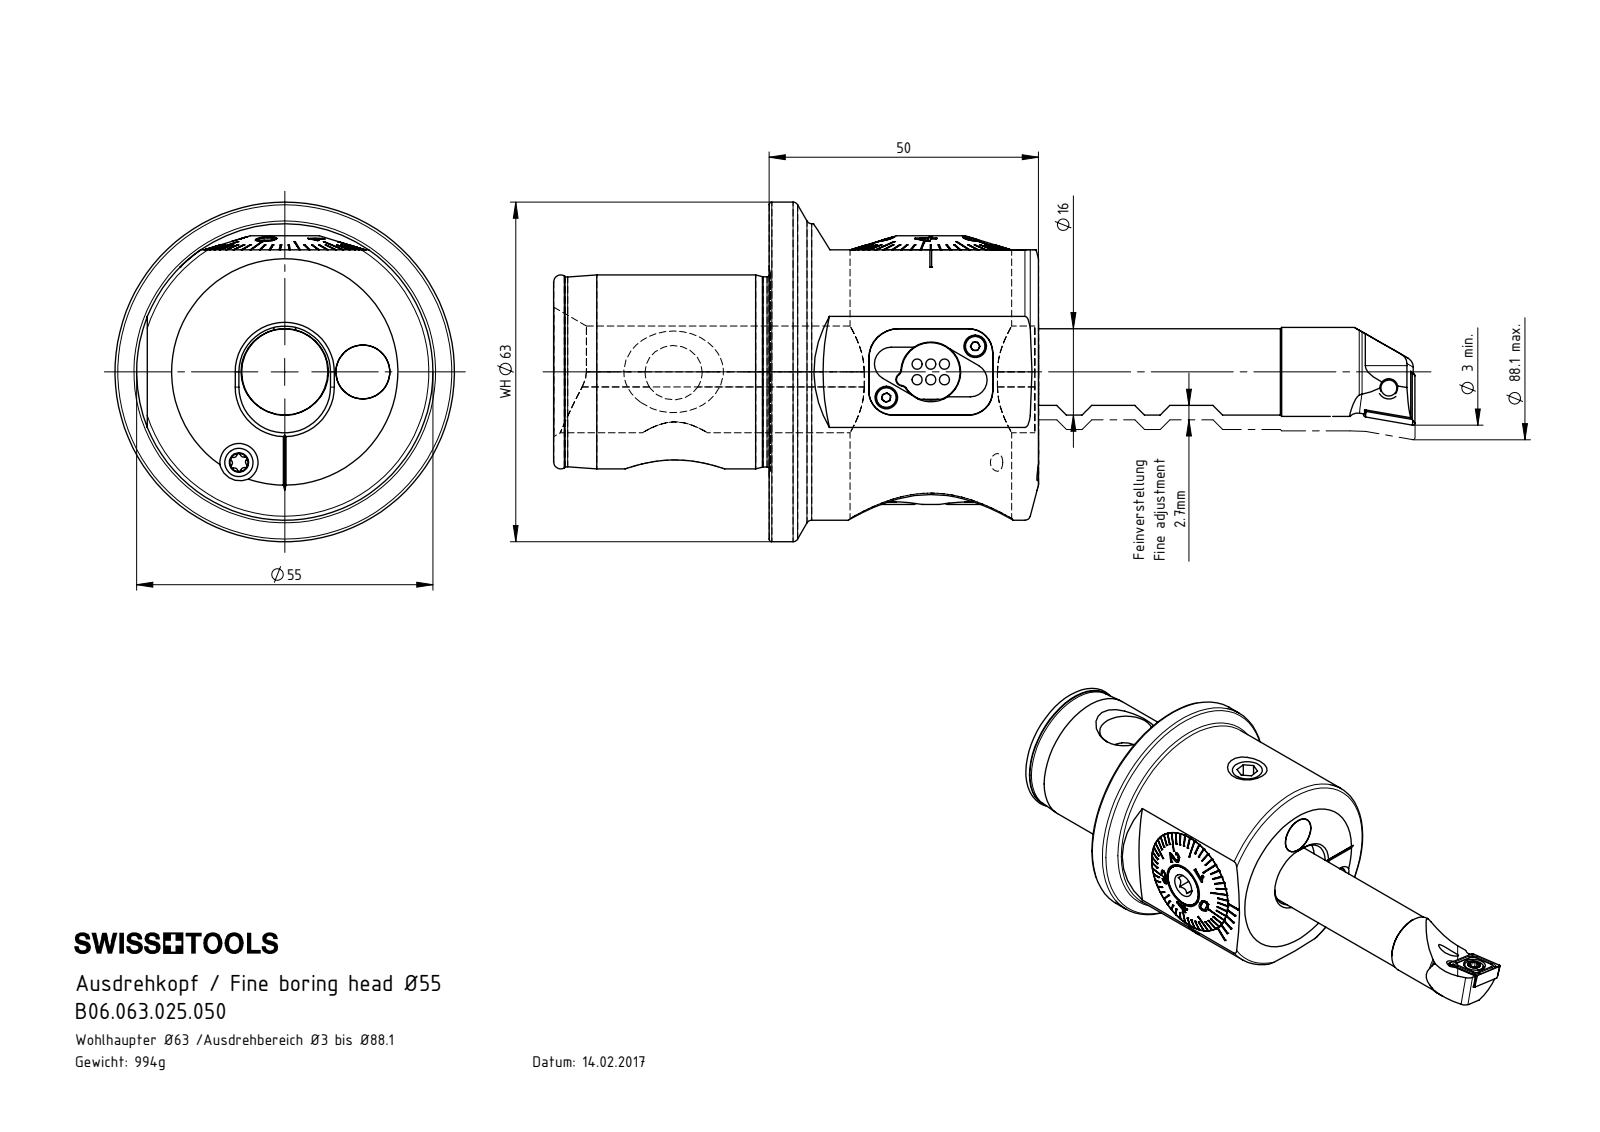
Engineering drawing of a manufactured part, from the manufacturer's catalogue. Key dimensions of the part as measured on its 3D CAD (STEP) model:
Part name (STEP PRODUCT): A55-BG3.011.033_A_gekrzt; A55-BG2.012.006_B; B20-WCB.K11.105; B06.063.025.050 (+8 more)
STEP written by: SolidWorks 2015 (AUTOMOTIVE_DESIGN)
Units: millimetres
Bodies: 25 solids, 1084 faces (450 planar, 250 cylindrical, 384 other)
Overall size (bounding box): 159.88 × 63 × 63
Volume: 146 335 mm³ · Surface area: 52 595 mm²
Round holes (diameter × count): ⌀3.2 ×4, ⌀1.6 ×3, ⌀3.3 ×3, ⌀4.2 ×3, ⌀8.5 ×3, ⌀2.2 ×2, ⌀3 ×2, ⌀4.4 ×1, ⌀6.1 ×1, ⌀8 ×1, ⌀9.5 ×1, ⌀10 ×1
Round bosses / shafts (diameter × count): ⌀1.9 ×6, ⌀10 ×3, ⌀5.25 ×2, ⌀4 ×2, ⌀3.8 ×2, ⌀2 ×2, ⌀63 ×1, ⌀55 ×1
Partial cylindrical surfaces — rounded edges, fillets, slot ends (radius × count): R0.34 ×12, R0.59 ×12, R1.2 ×8, R1.1 ×6, R4.5 ×4, R3.2 ×3, R4.4 ×3, R3.1 ×2
Main face-to-face distances: 50, 3.7, 4, 1.2, 5.65, 6.85, 3.15, 2.5, 5.3, 2.8
Hole centre spacings: 4.1, 4.32, 7.25, 8.45, 9.52, 12, 12.68, 14.5
